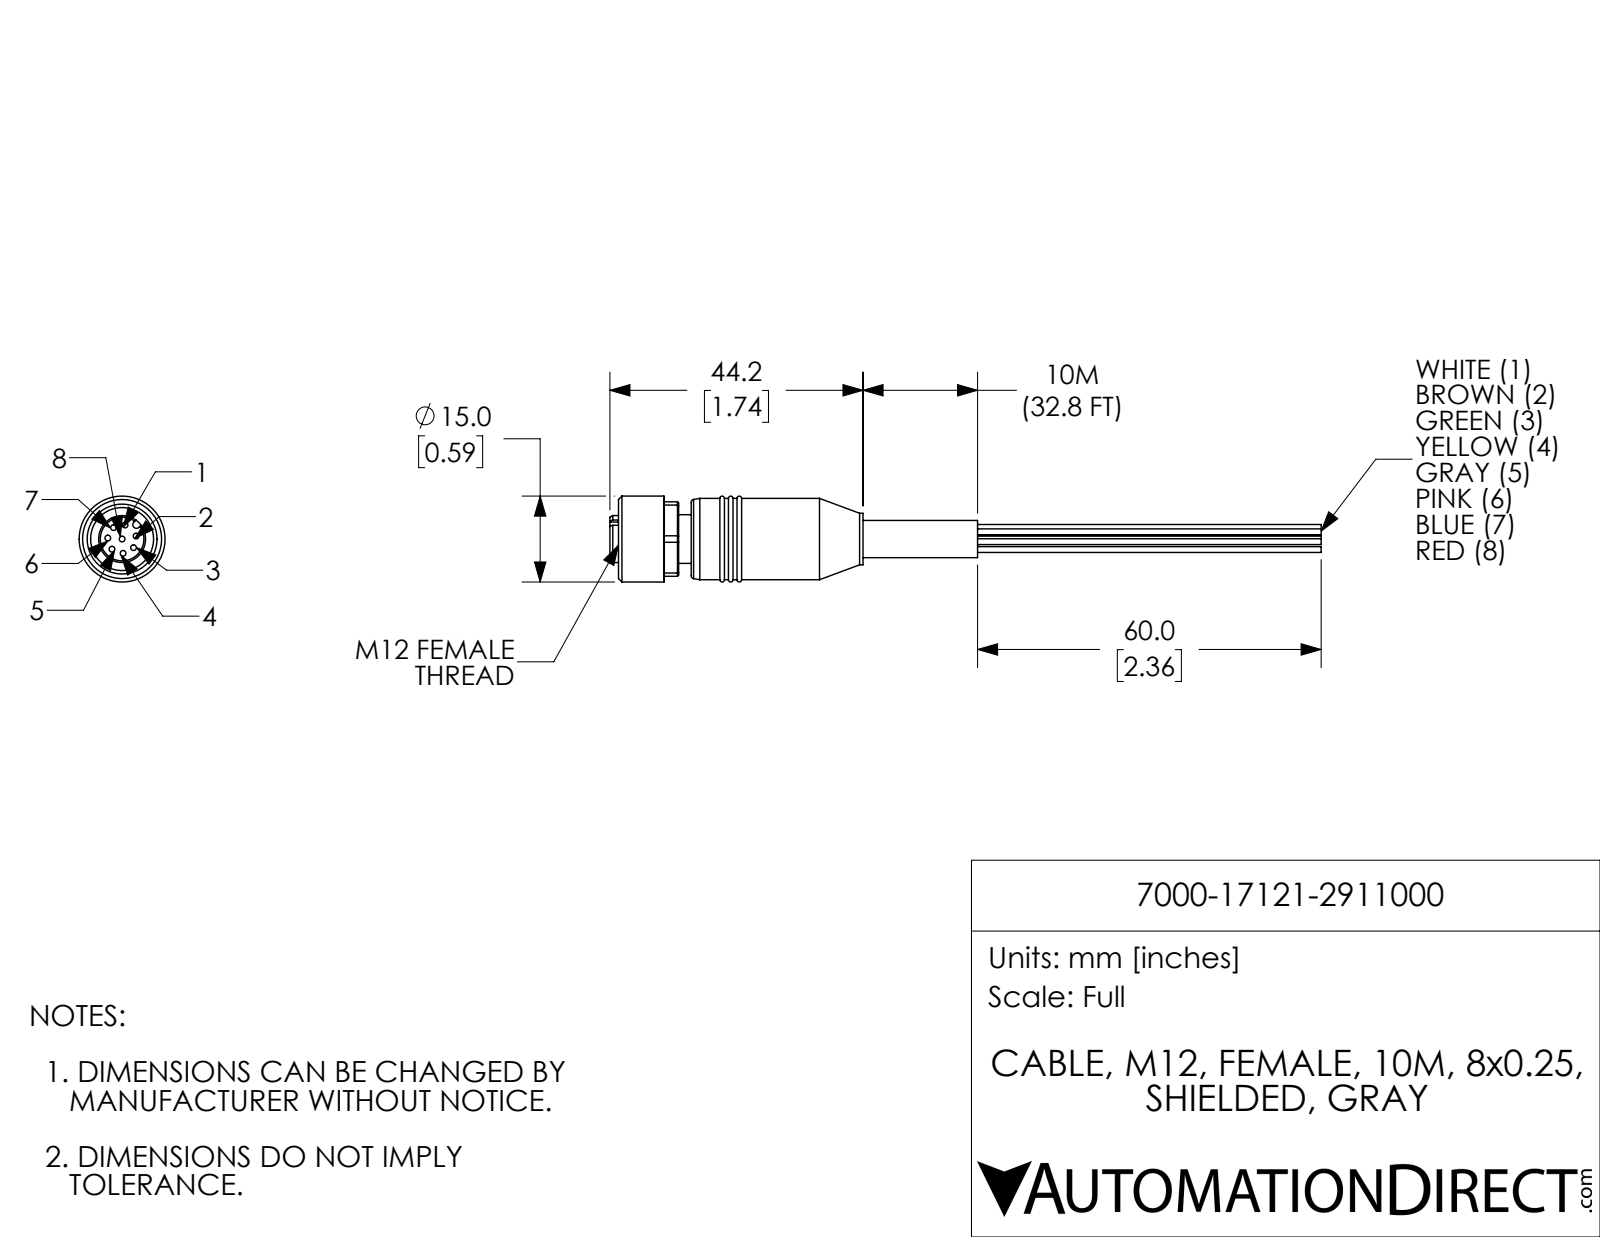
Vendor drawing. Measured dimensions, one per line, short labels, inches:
name: 7000-17121-2911000
written by: SolidWorks 2017 (AUTOMOTIVE_DESIGN)
unit: in
bodies: 1 solid, 131 faces (39 planar, 59 cylindrical, 33 other)
size: 4.89 × 0.591 × 0.591
volume: 0.428 in³; area: 7.634 in²
holes: 8× ⌀0.039, 1× ⌀0.433
bosses: 8× ⌀0.04, 1× ⌀0.591, 1× ⌀0.559, 1× ⌀0.354, 1× ⌀0.335, 1× ⌀0.323, 1× ⌀0.256
rounds: 1× R0.026, 1× R0.283
face distances: 0.087, 0.512, 0.118, 0.205, 0.354, 0.472, 0.559, 0.098, 0.059, 0.295
hole spacings: 0.098, 0.081, 0.149, 0.195, 0.082, 0.166, 0.189, 0.189
